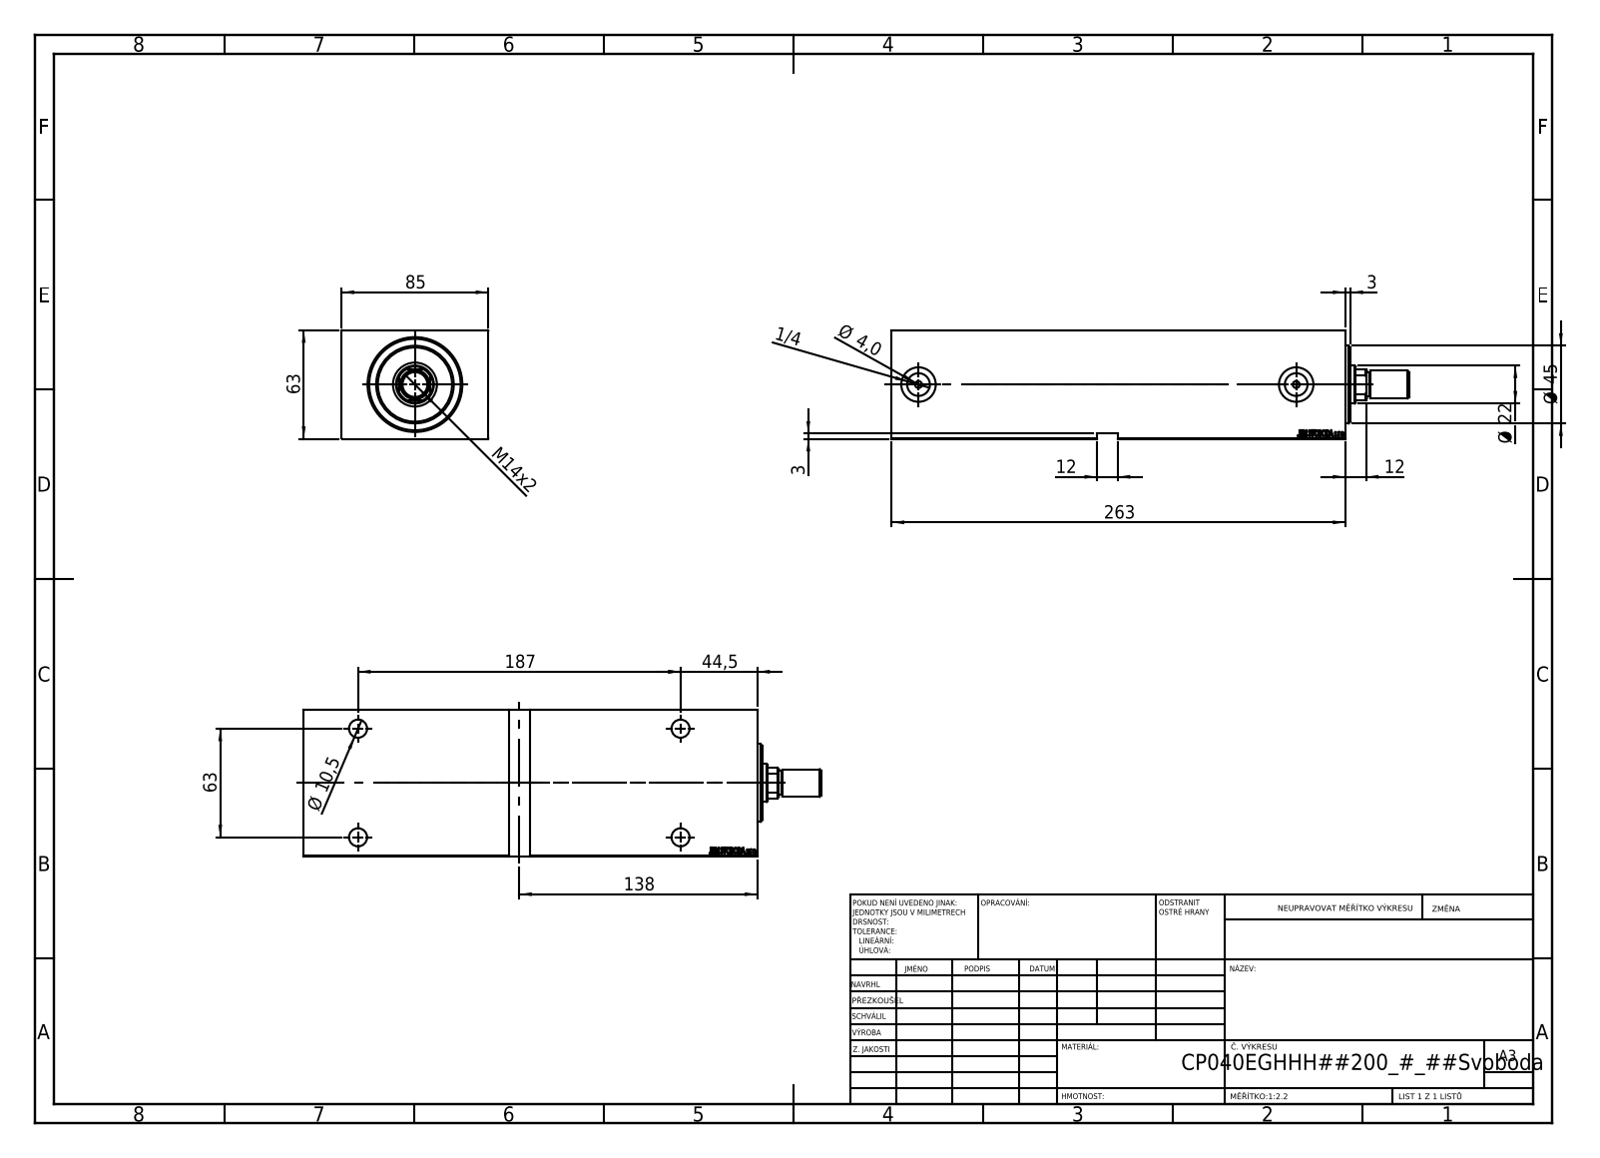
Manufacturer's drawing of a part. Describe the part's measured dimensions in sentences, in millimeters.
The part is named "V450CM_E_VCP; V450CM_E_Body; V450CM_VC_B; V450CM_MALE_METRIC". Its 3-D file was written by "SolidWorks 2019 (CONFIG_CONTROL_DESIGN)". It is 4 solids with 870 faces: 414 planar, 56 cylindrical and 400 other. Overall it measures 300 by 85 by 63 millimeters. Its volume is 1 211 000 cubic millimeters and its surface area 163 864 square millimeters. Round holes: 4 of diameter 10.5, 4 of diameter 16.5, 2 of diameter 4, 2 of diameter 13.16, 2 of diameter 20, 1 of diameter 12.5, 1 of diameter 22, 1 of diameter 25.5, 1 of diameter 40, 1 of diameter 53. Round bosses or shafts: 1 of diameter 45, 1 of diameter 42, 1 of diameter 16, 1 of diameter 14. Partial cylindrical surfaces (rounded edges, fillets, slot ends): 1 of radius 10.5. The main face-to-face distances are 63, 85, 263, 12, 251, 3, 5, 258, 246, 60. The hole center spacings are 63, 187, 197.33, 219.
